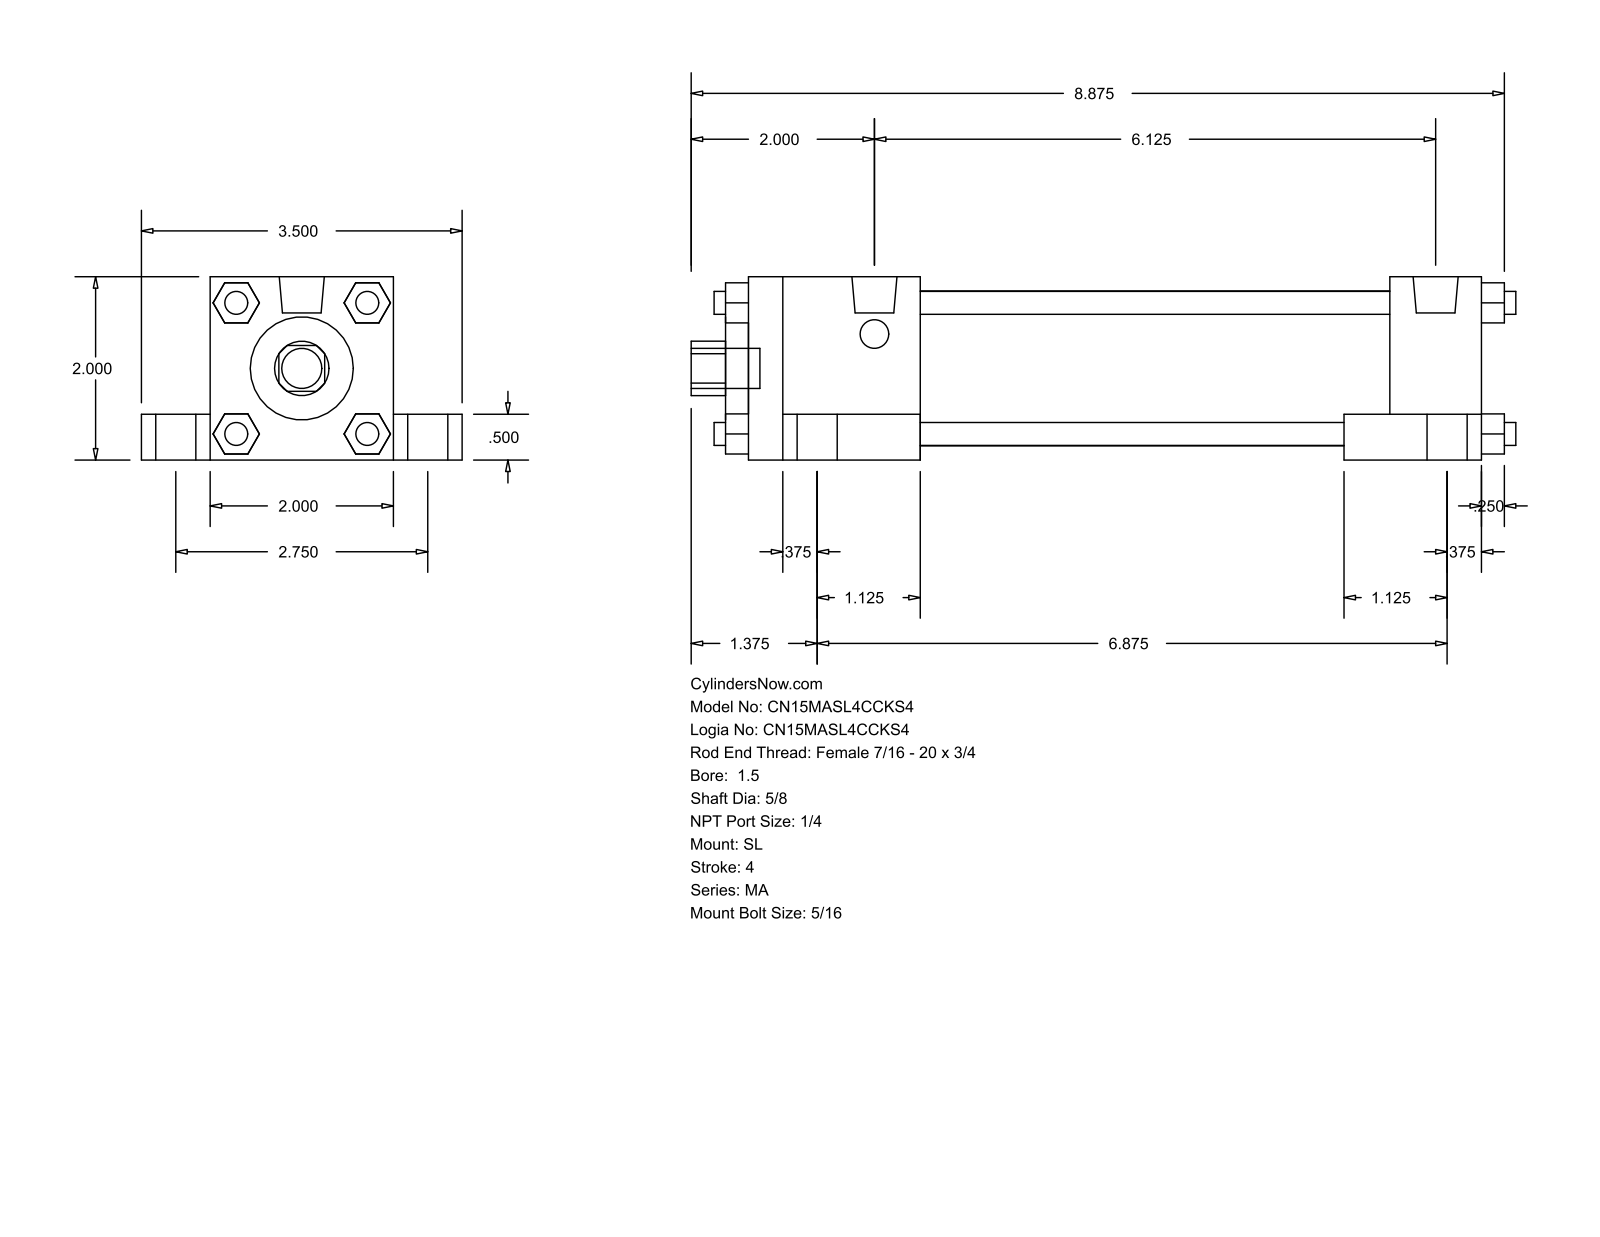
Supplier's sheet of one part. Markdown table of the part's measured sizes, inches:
| quantity | value |
| --- | --- |
| part name | MA_SL__0150_0.625 |
| STEP written by | GSSL Pune (CONFIG_CONTROL_DESIGN) |
| units | inches |
| bodies | 0 solids, 148 faces (112 planar, 36 cylindrical, 0 other) |
| overall size | 9 × 3.5 × 2 |
| round holes (diameter × count) | 0.625 × 1, 1.125 × 1, 1.69 × 1 |
| round bosses / shafts (diameter × count) | 0.437 × 5, 0.687 × 4, 0.313 × 4, 0.25 × 4, 0.492 × 2 |
| partial cylindrical surfaces (radius × count) | 0.297 × 1 |
| main face-to-face distances | 2, 0.75, 1.5, 0.5, 2.75, 8, 0.375, 7, 1, 1.875 |
